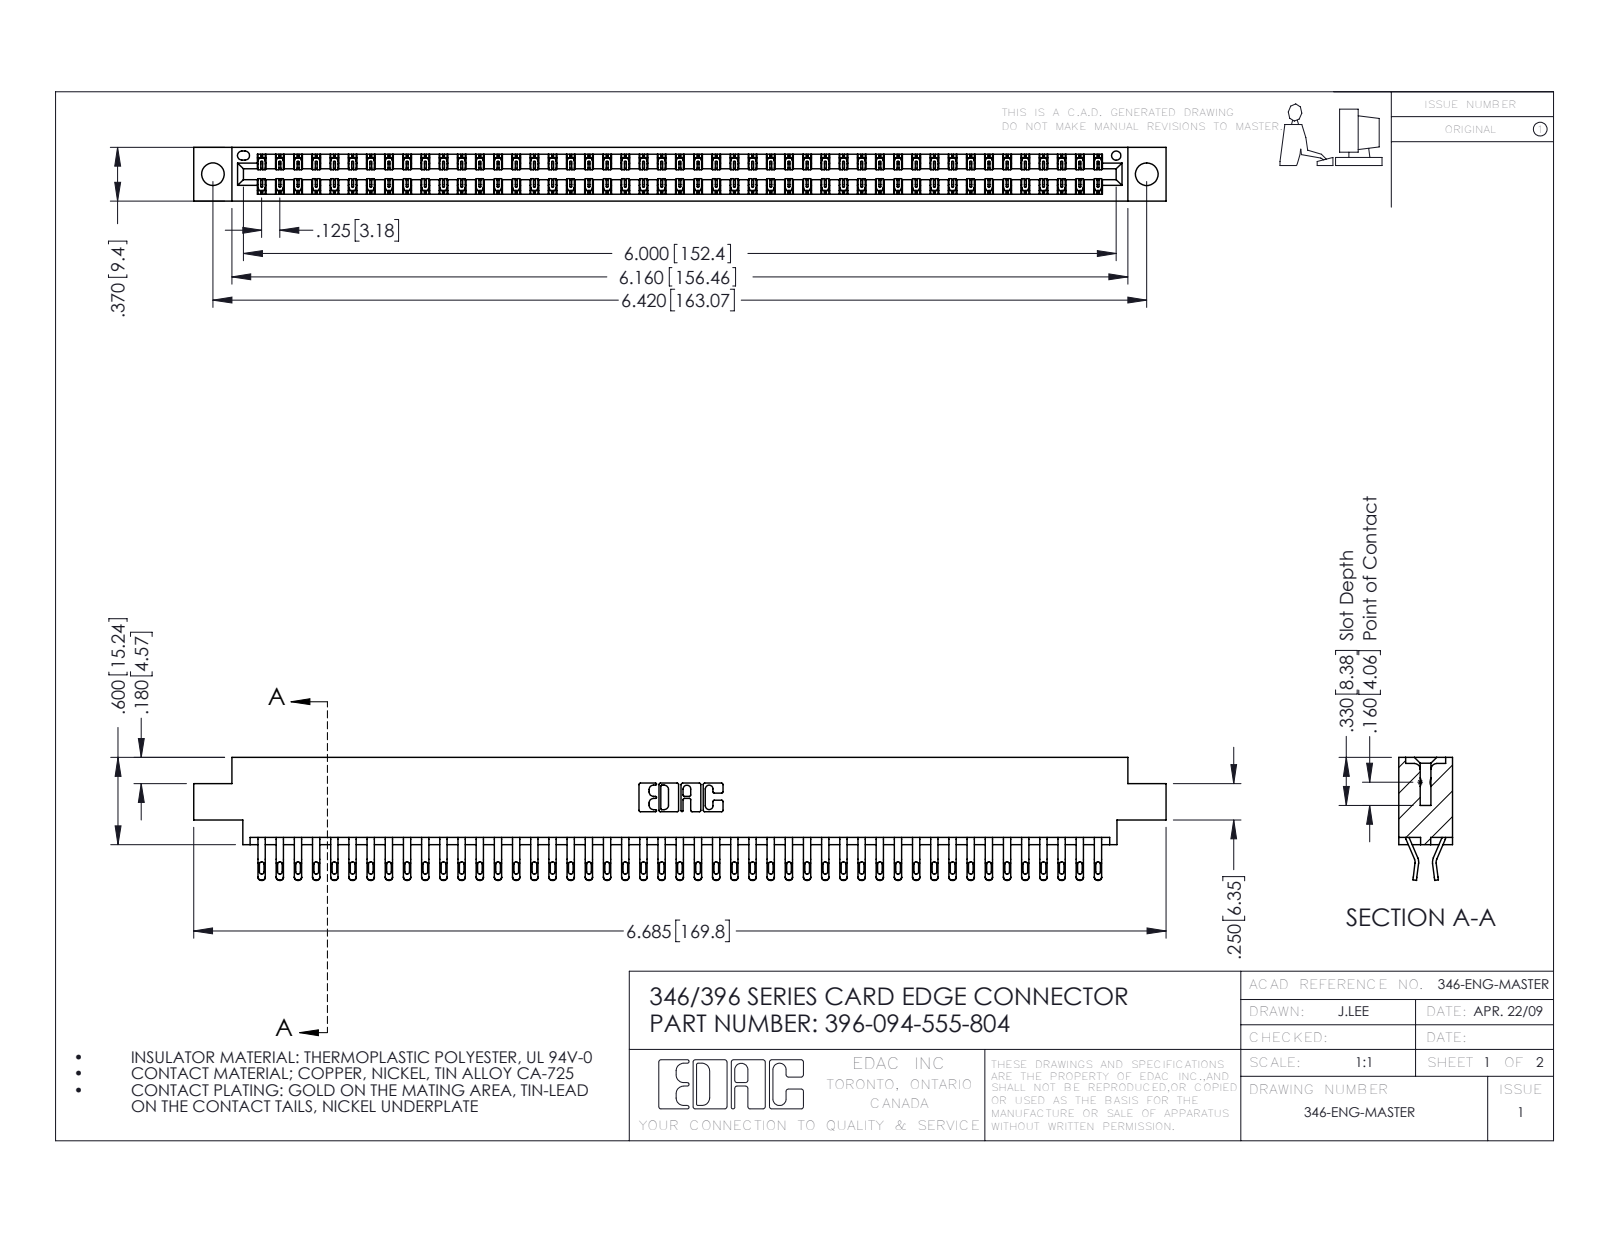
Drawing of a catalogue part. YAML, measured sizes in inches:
part_name: "396-094-555-804; 345-292-001_555 Tail; 346 Part_0.170 Offset - 0.156 Dia-TH"
step_written_by: "SolidWorks 2016 (CONFIG_CONTROL_DESIGN)"
units: inches
bodies: {solids: 95, faces: 5578, planar: 3182, cylindrical: 2396, other: 0}
overall_size: [6.685, 0.845, 0.37]
volume: 1.015
surface_area: 37.04
round_holes:
  - {diameter: 0.156, count: 2}
  - {diameter: 0.064, count: 1}
partial_cylinders:
  - {radius: 0.016, count: 188}
  - {radius: 0.02, count: 188}
  - {radius: 0.006, count: 141}
  - {radius: 0.01, count: 22}
  - {radius: 0.007, count: 6}
  - {radius: 0.031, count: 6}
  - {radius: 0.026, count: 3}
  - {radius: 0.01, count: 2}
face_to_face_distances: [0.048, 0.322, 0.37, 0.25, 0.025, 0.072, 0.298, 0.275, 0.148, 0.222]
hole_center_spacings: [0.246, 6.211, 6.42]
